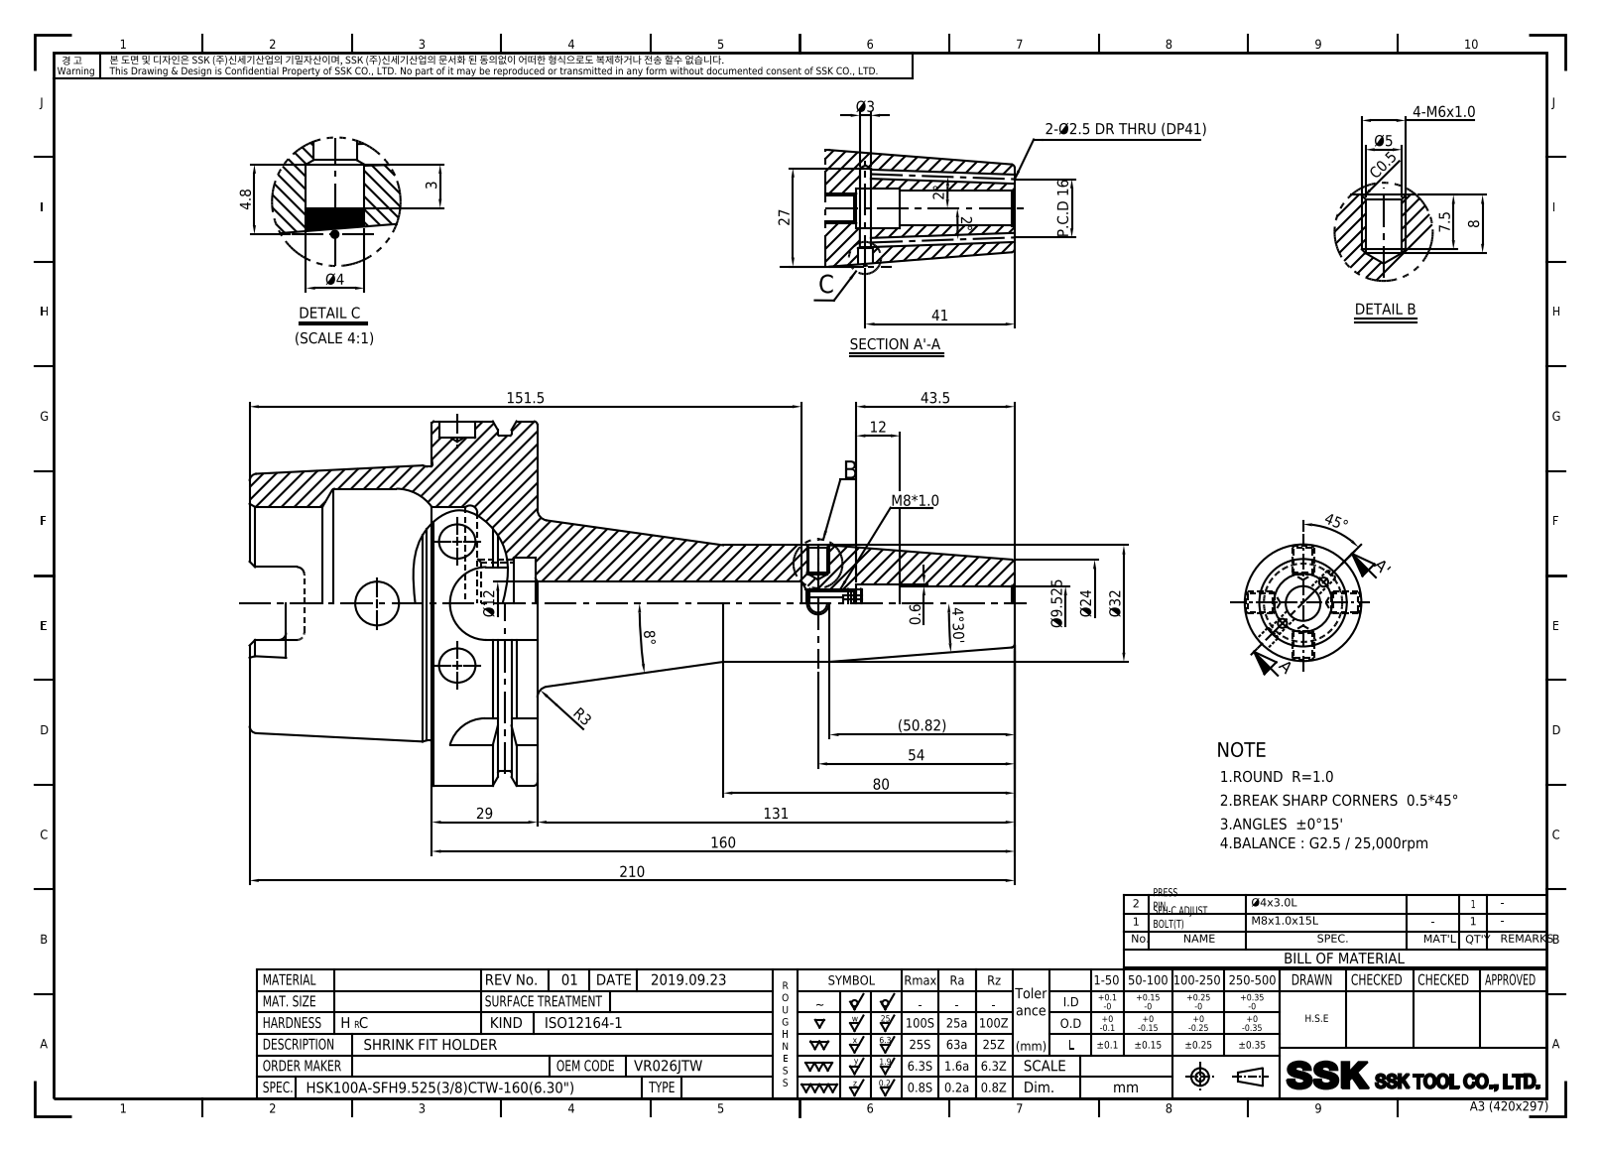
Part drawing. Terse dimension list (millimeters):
name: LO-HSK100A-SFH9.525CTW-160
written by: Autodesk Inventor 2022 (AUTOMOTIVE_DESIGN)
unit: mm
bodies: 1 solid, 120 faces (38 planar, 37 cylindrical, 45 other)
size: 210 × 100 × 100
volume: 363 511 mm³; area: 66 162 mm²
holes: 2× ⌀2.5, 1× ⌀6.92, 1× ⌀8, 1× ⌀9.52, 1× ⌀10, 1× ⌀10.72, 1× ⌀12, 1× ⌀22.38, 1× ⌀25, 1× ⌀53, 1× ⌀63
bosses: 1× ⌀100, 1× ⌀92, 1× ⌀75.41, 1× ⌀32
rounds: 6× R2, 4× R4.88, 4× R10
face distances: 29, 12.5, 16.5, 62.5, 50, 79, 88, 78.5, 28.5, 16
